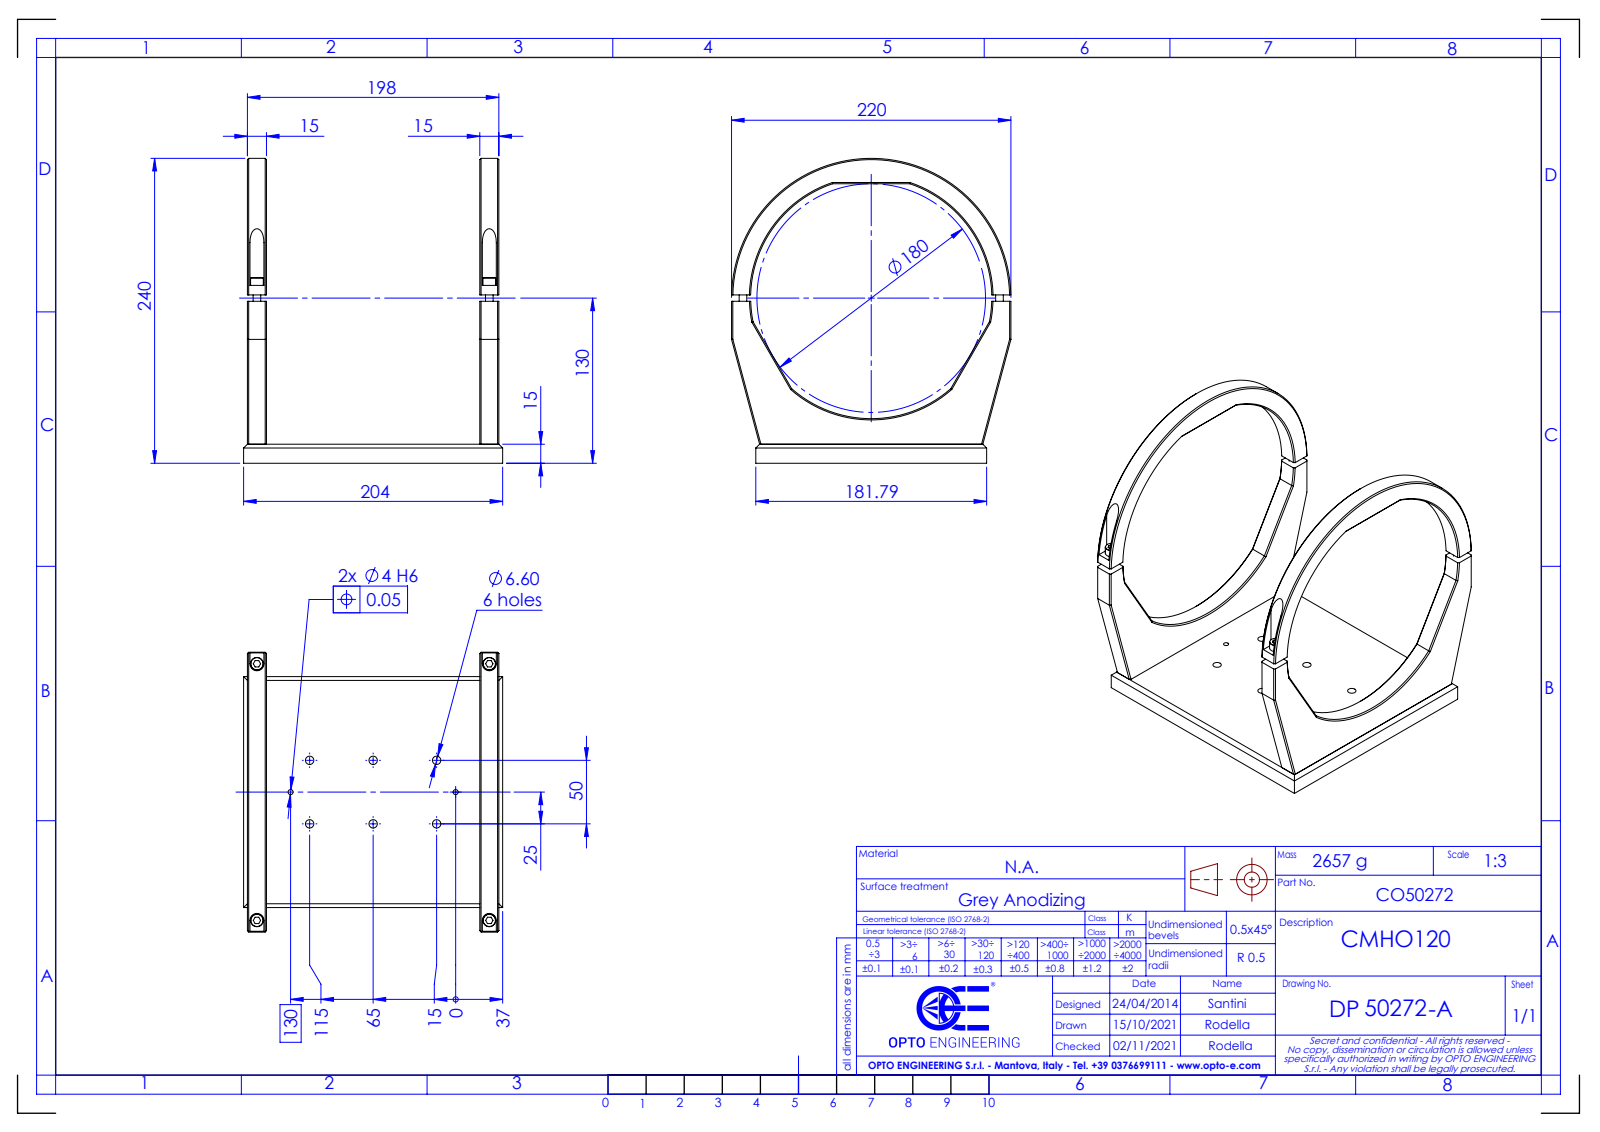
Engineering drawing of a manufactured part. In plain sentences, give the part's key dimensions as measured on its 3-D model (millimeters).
The part is named "DP50272-A_CMHO120". Its 3-D file was written by "SolidWorks 2021 (CONFIG_CONTROL_DESIGN)". It is 0 solids with 224 faces: 128 planar, 56 cylindrical and 40 other. Overall it measures 240 by 220 by 204 millimeters. Round holes: 6 of diameter 6.6, 4 of diameter 11, 2 of diameter 4. Round bosses or shafts: 4 of diameter 10, 4 of diameter 6. Partial cylindrical surfaces (rounded edges, fillets, slot ends): 4 of radius 5.5, 1 of radius 94.91, 1 of radius 95, 1 of radius 110. The main face-to-face distances are 15, 183, 198, 168, 181.78, 220, 3, 18, 186, 201. The hole center spacings are 50, 29.15, 69.64, 70.71, 117.69, 130, 57.63, 57.65.
